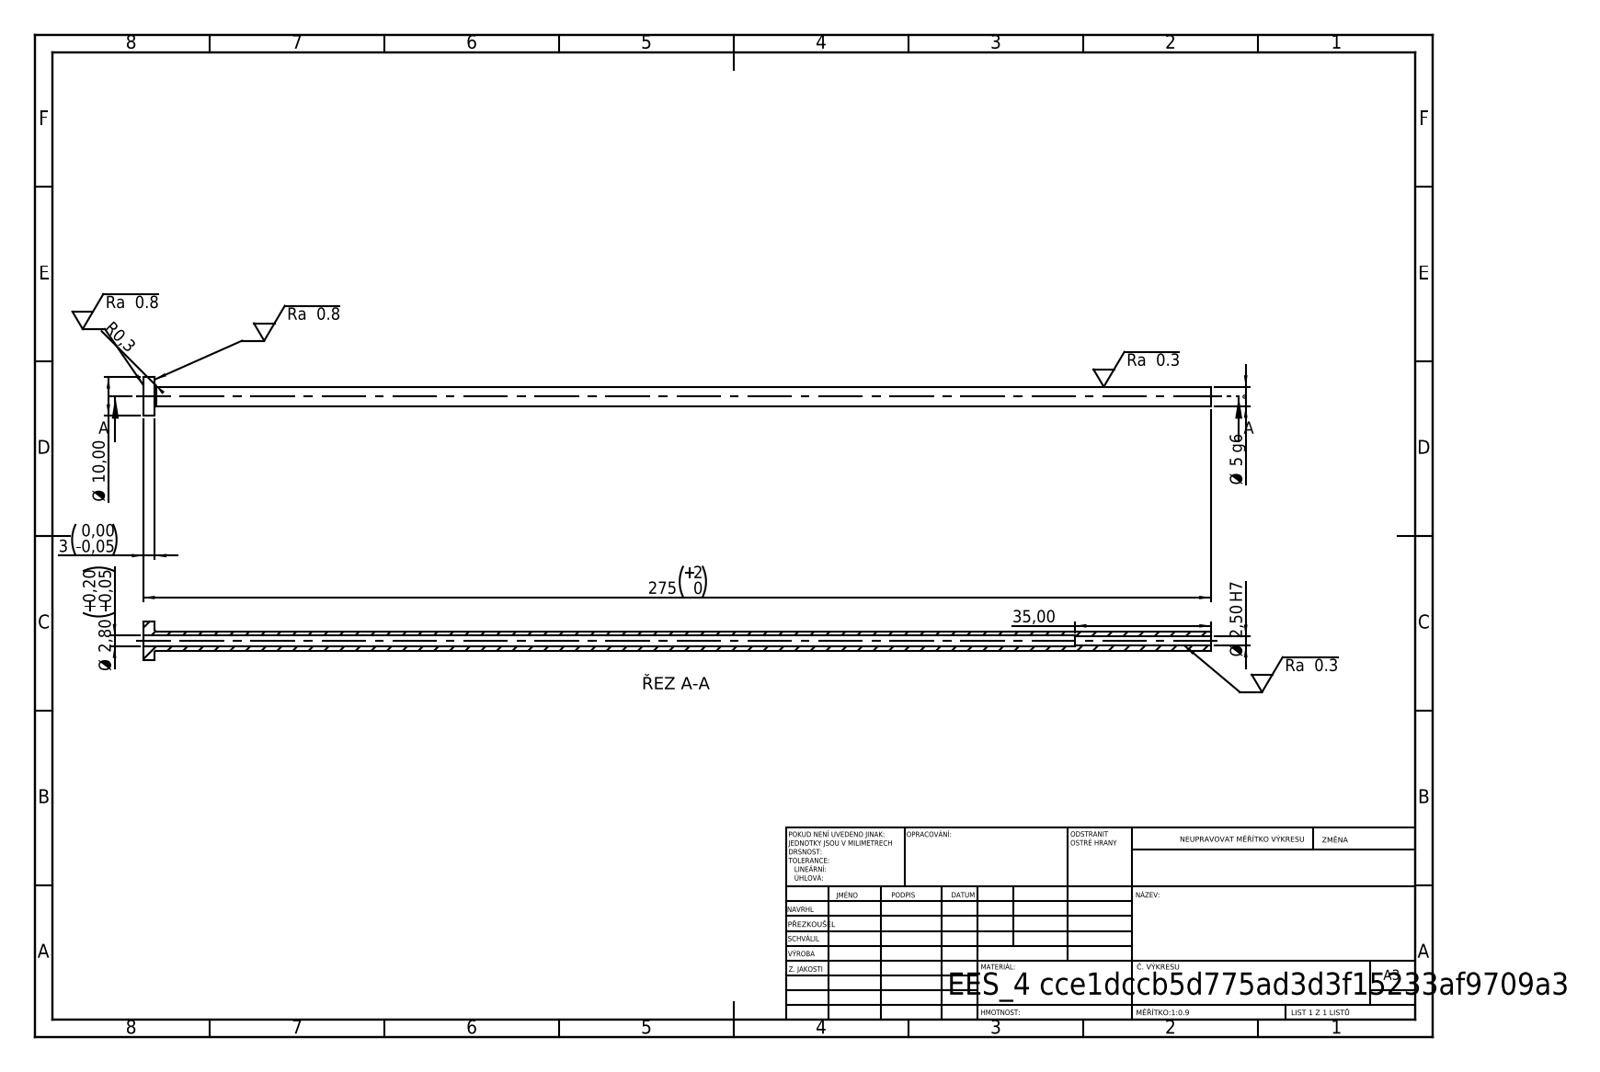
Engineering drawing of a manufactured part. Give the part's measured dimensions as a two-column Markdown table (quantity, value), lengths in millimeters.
| quantity | value |
| --- | --- |
| STEP written by | SolidWorks 2019 (CONFIG_CONTROL_DESIGN) |
| units | millimeters |
| bodies | 1 solid, 14 faces (4 planar, 8 cylindrical, 2 other) |
| overall size | 275 × 10 × 10 |
| volume | 3 927 mm³ |
| surface area | 6 898 mm² |
| round holes (diameter × count) | 2.5 × 1, 2.8 × 1 |
| round bosses / shafts (diameter × count) | 10 × 1, 5 × 1 |
| main face-to-face distances | 3, 275, 272, 240, 237, 35 |
